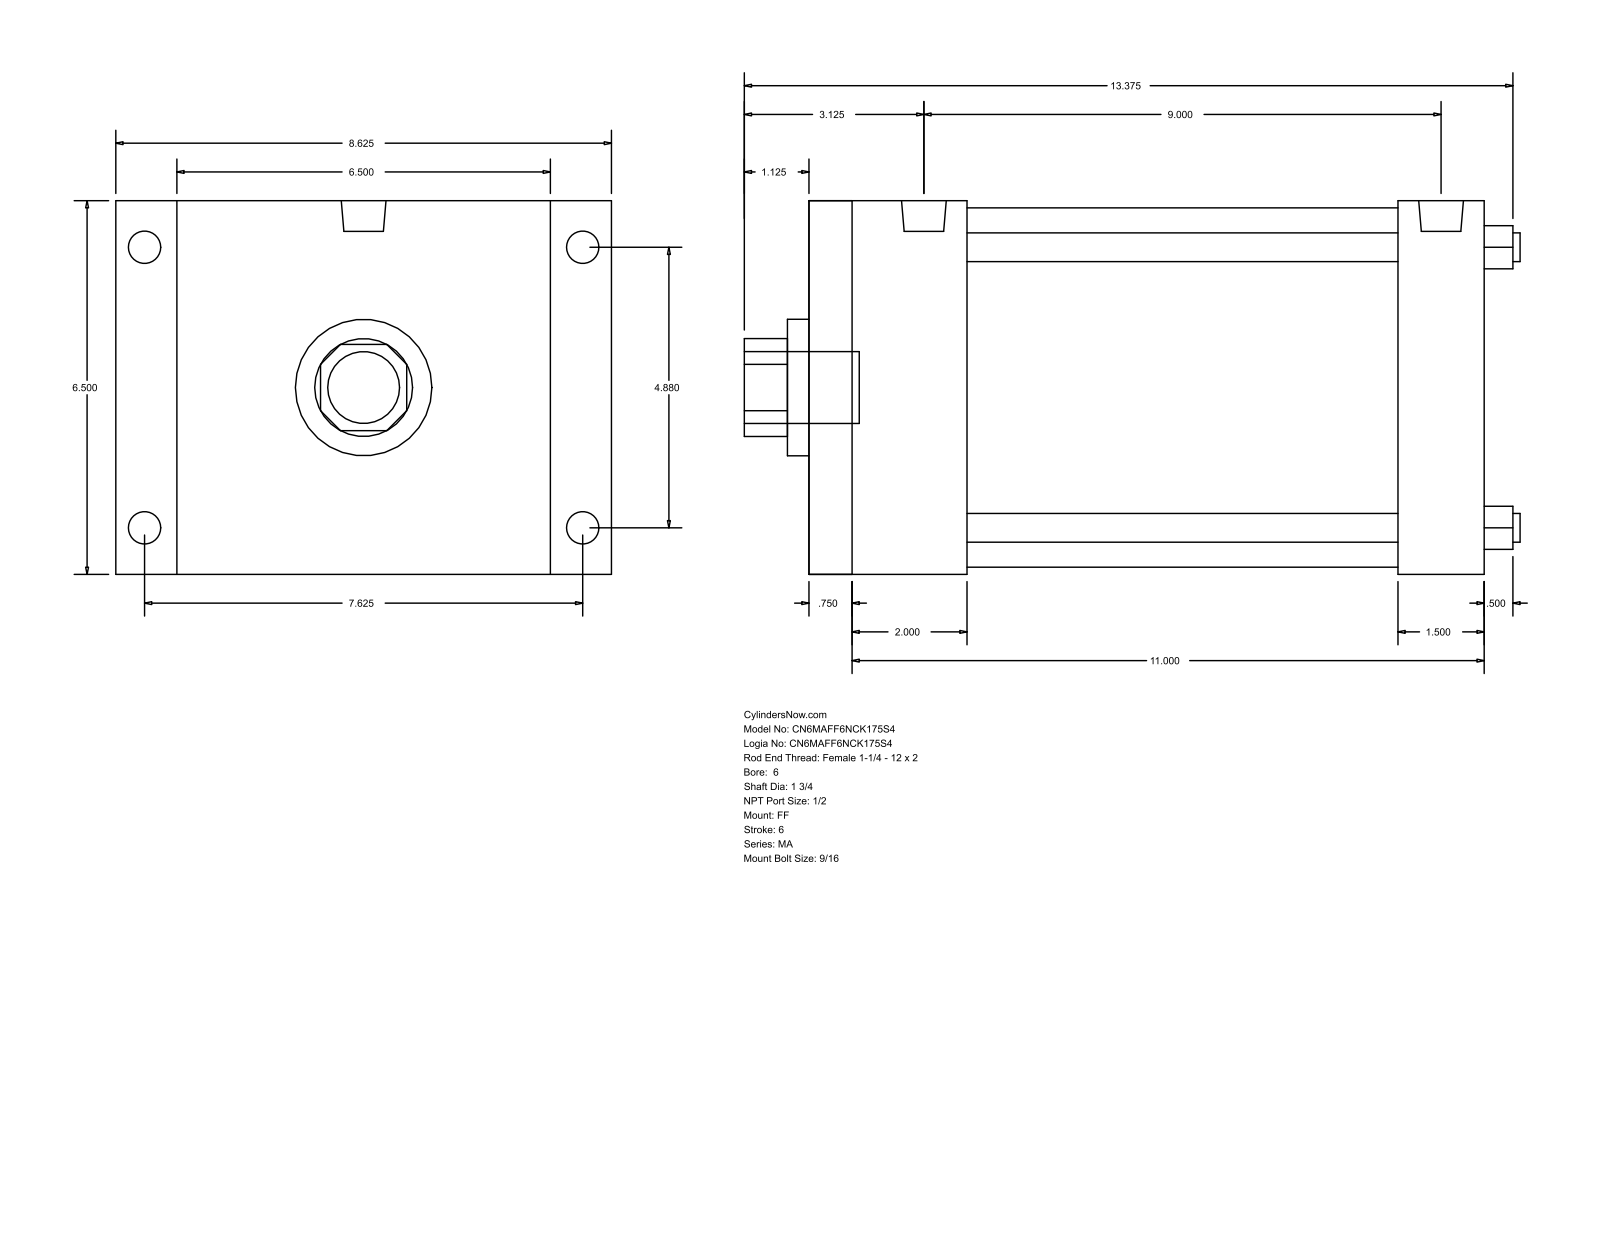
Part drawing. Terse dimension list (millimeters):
name: MA_FF__0600_1.75
written by: GSSL Pune (CONFIG_CONTROL_DESIGN)
unit: mm
bodies: 0 solids, 92 faces (64 planar, 28 cylindrical, 0 other)
size: 342.9 × 219.07 × 165.1
holes: 4× ⌀12.7, 1× ⌀44.45, 1× ⌀60.33, 1× ⌀158.75
bosses: 4× ⌀17.46, 4× ⌀14.29, 2× ⌀19.77, 1× ⌀31.75
rounds: 1× R21.63
face distances: 165.1, 298.45, 19.05, 279.4, 50.8, 241.31, 69.85, 228.6, 260.36, 190.51
hole spacings: 87.65, 123.96, 175.31
